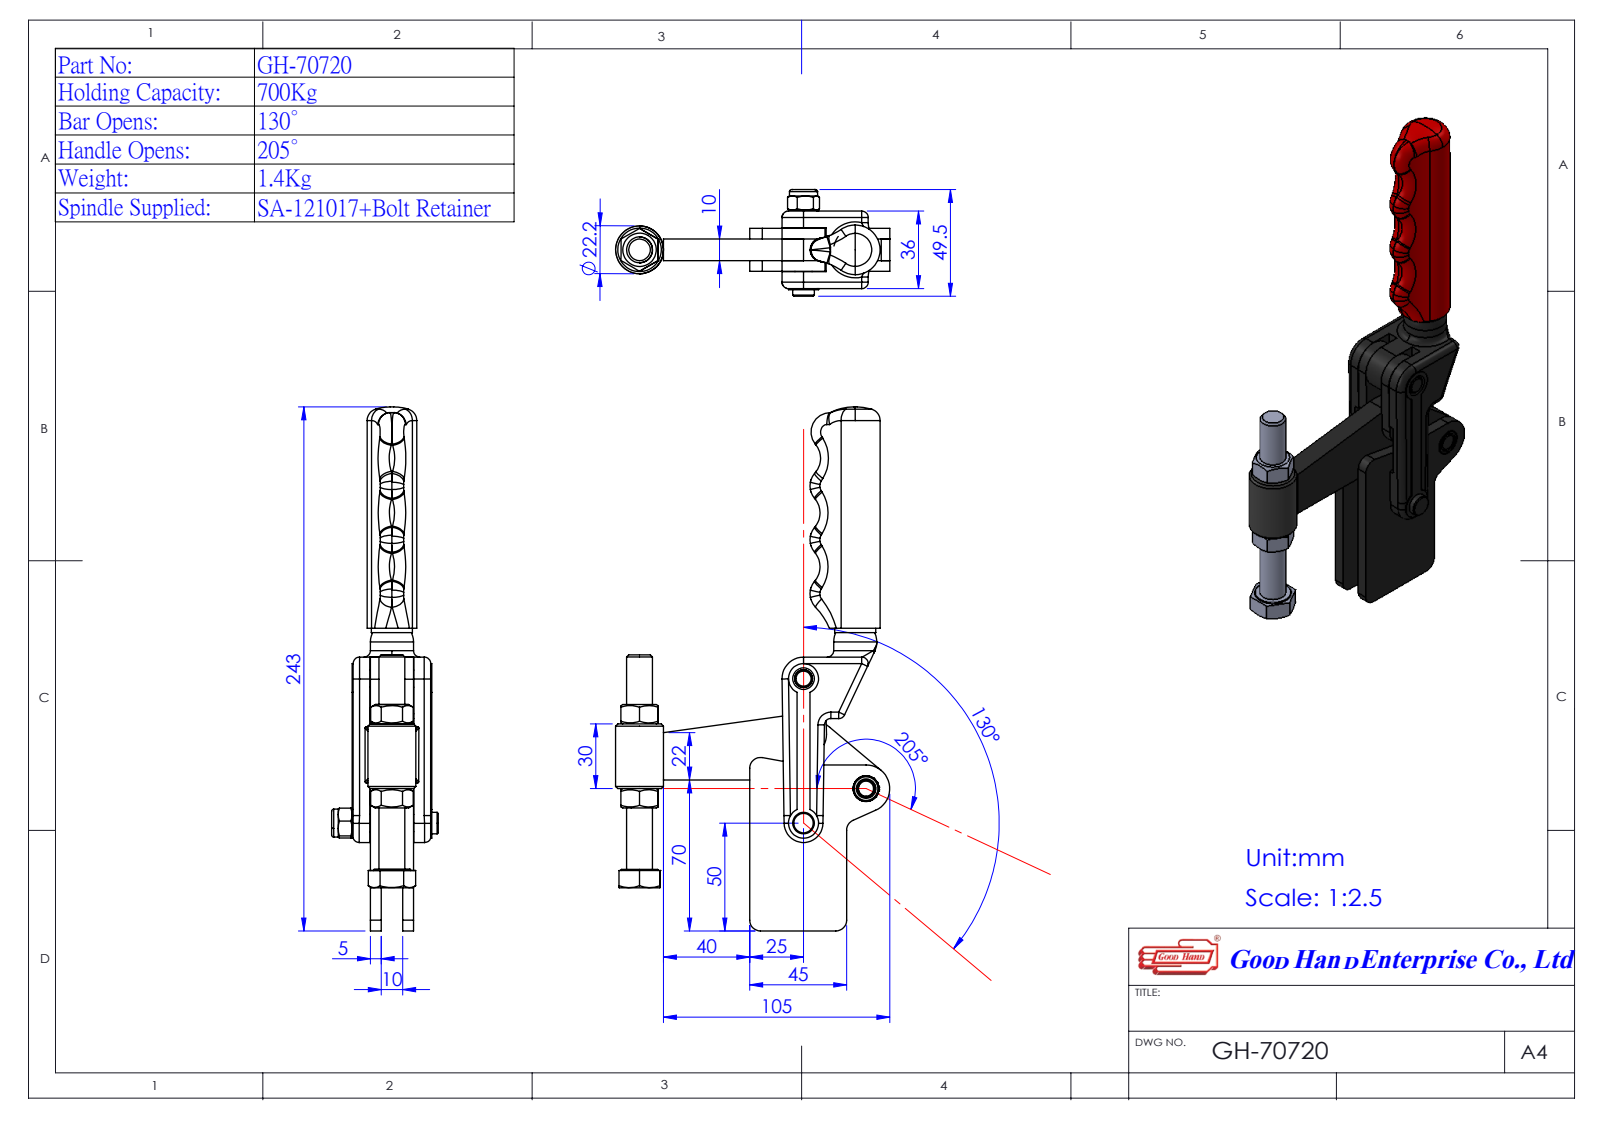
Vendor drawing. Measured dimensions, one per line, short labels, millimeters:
name: Group5^GH-70720(簡化)-1; Group3^GH-70720(簡化)-1; 4701764-1^GH-70720(簡化)-1; Group4^GH-70720(簡化)-1 (+3 more)
written by: SolidWorks 2016 (AUTOMOTIVE_DESIGN)
unit: mm
bodies: 6 solids, 342 faces (102 planar, 116 cylindrical, 124 other)
size: 243.02 × 129 × 46.44
volume: 199 073 mm³; area: 65 186 mm²
holes: 4× ⌀6, 1× ⌀12
bosses: 2× ⌀14, 2× ⌀6, 1× ⌀22.2, 1× ⌀20, 1× ⌀19.05, 1× ⌀18, 1× ⌀12, 1× ⌀10
rounds: 13× R3, 7× R10, 7× R30, 5× R9, 4× R5, 3× R25, 2× R11, 1× R11.53
face distances: 5, 15, 10, 20, 5.15, 15.15, 20.15, 28, 0.5, 13
hole spacings: 25.99, 32.47, 37.78, 41.01, 58.3, 67
